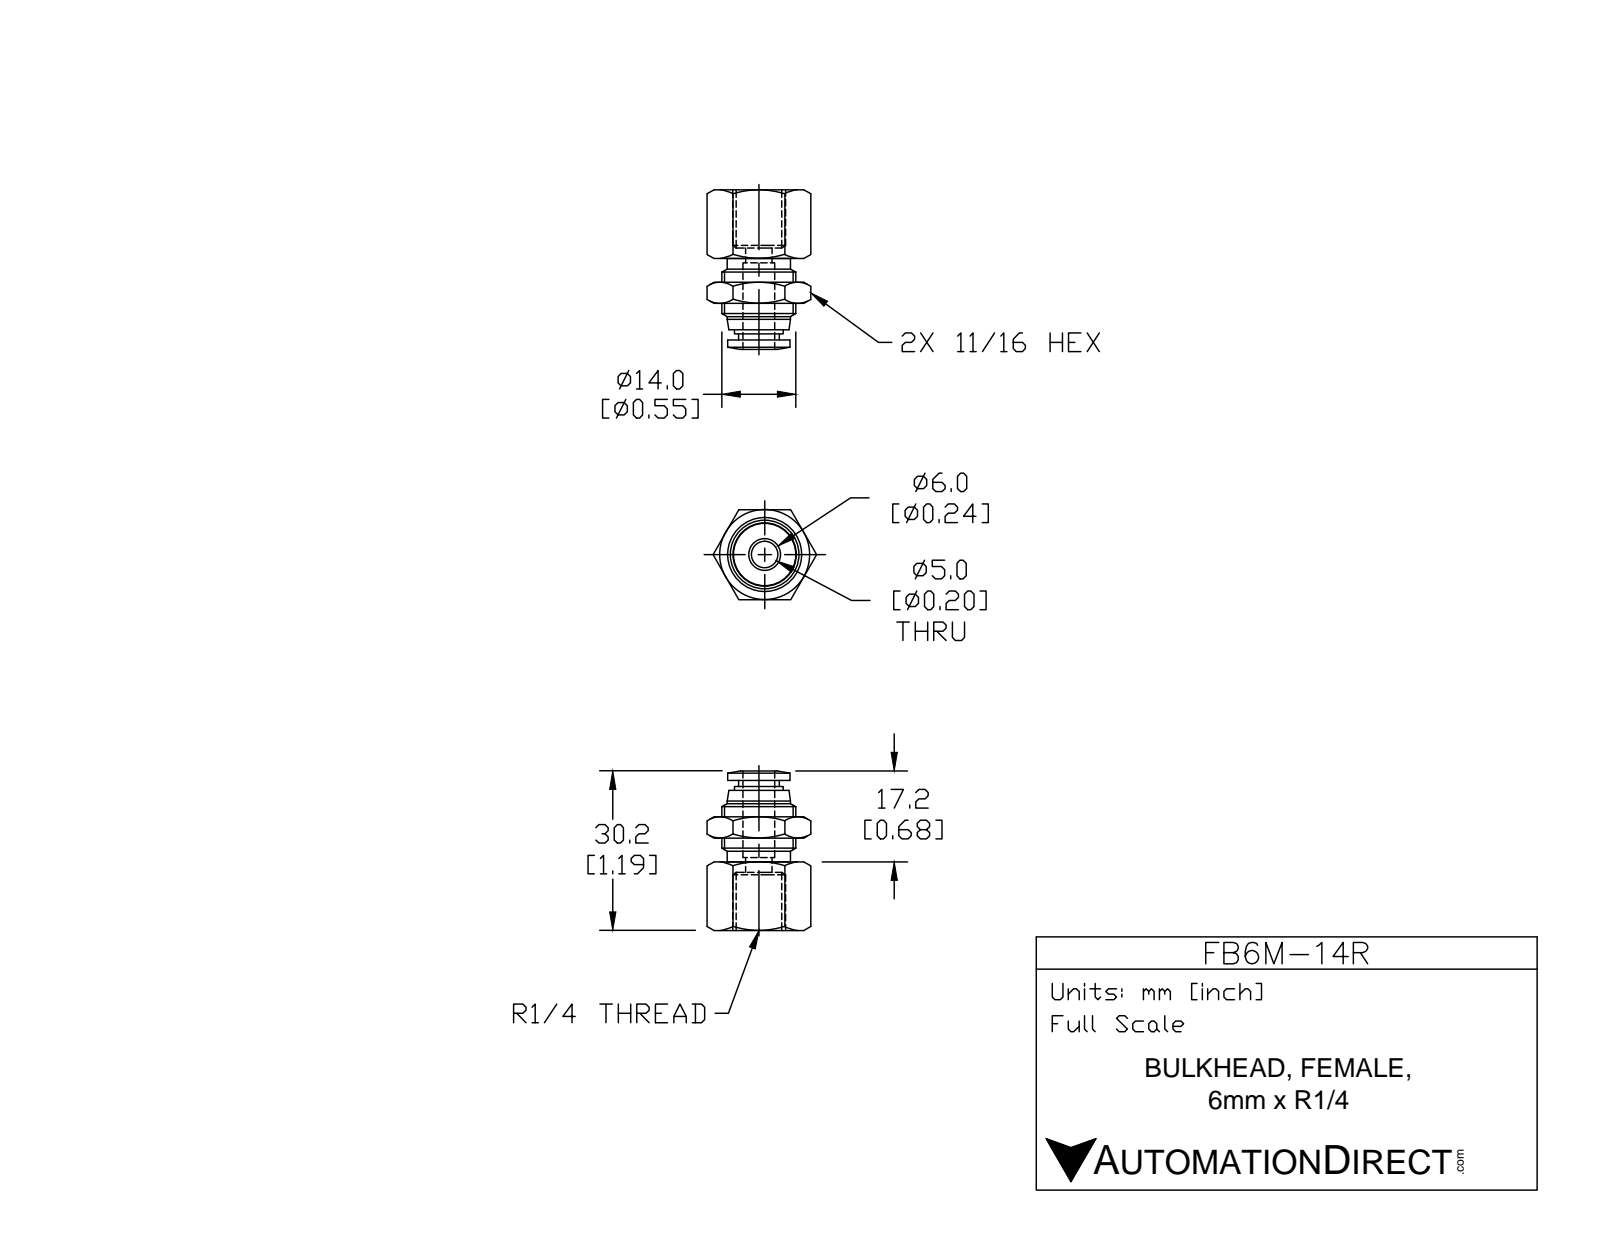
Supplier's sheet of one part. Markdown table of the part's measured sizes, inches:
| quantity | value |
| --- | --- |
| part name | FB6M-14R |
| STEP written by | SolidWorks 2015 (AUTOMOTIVE_DESIGN) |
| units | inches |
| bodies | 1 solid, 80 faces (22 planar, 18 cylindrical, 40 other) |
| overall size | 1.189 × 0.773 × 0.669 |
| volume | 0.23 in³ |
| surface area | 4.731 in² |
| round holes (diameter × count) | 0.197 × 1, 0.248 × 1 |
| round bosses / shafts (diameter × count) | 0.551 × 1, 0.472 × 1, 0.465 × 1, 0.362 × 1, 0.303 × 1 |
| main face-to-face distances | 0.669, 0.079, 0.433, 0.512, 0.837, 0.404, 0.325, 0.679, 0.246, 0.167 |
